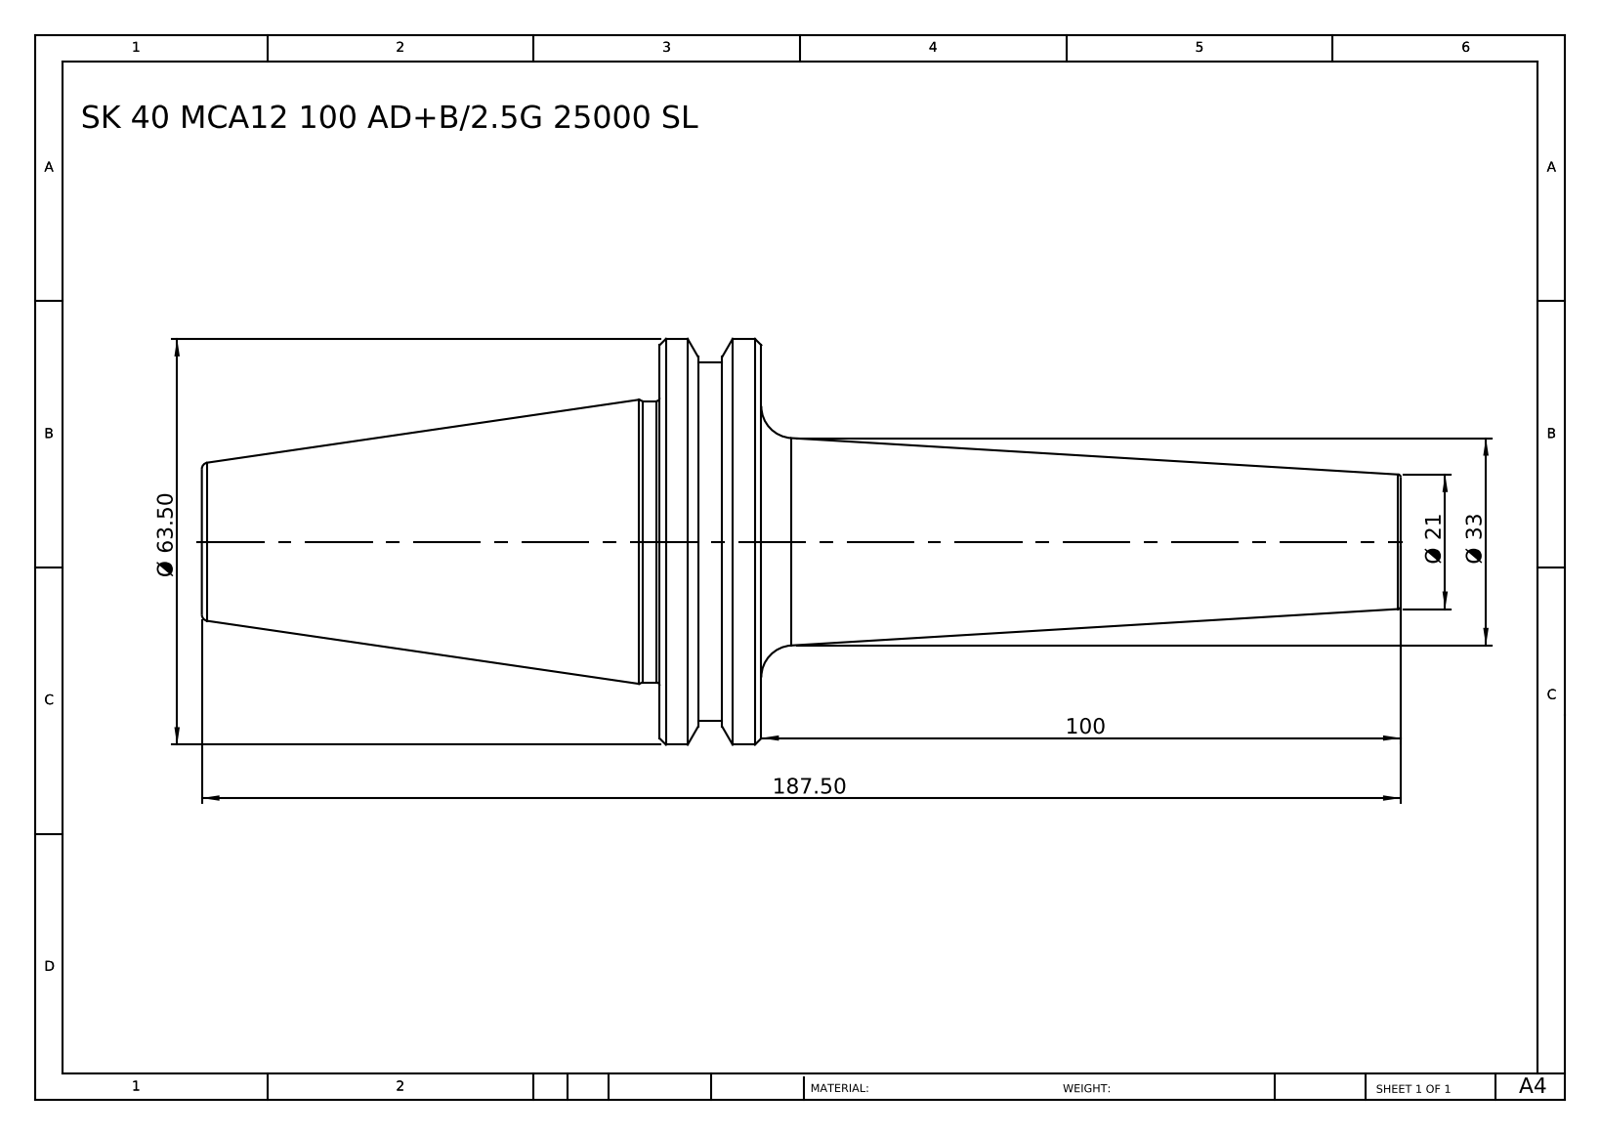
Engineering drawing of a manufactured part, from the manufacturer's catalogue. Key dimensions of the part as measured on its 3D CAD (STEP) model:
Part name (STEP PRODUCT): SK 40 MCA12 100 AD+B-2.5G 25000 SL
STEP written by: SolidWorks 2014 (CONFIG_CONTROL_DESIGN)
Units: millimetres
Bodies: 1 solid, 36 faces (6 planar, 8 cylindrical, 22 other)
Overall size (bounding box): 187.5 × 63.5 × 63.5
Volume: 175 816 mm³ · Surface area: 24 738 mm²
Round bosses / shafts (diameter × count): ⌀63.5 ×1, ⌀56 ×1, ⌀44 ×1
Main face-to-face distances: 15.9, 87.5, 71.6, 100, 115.9, 187.5, 109.9, 9.9, 6, 77.6
